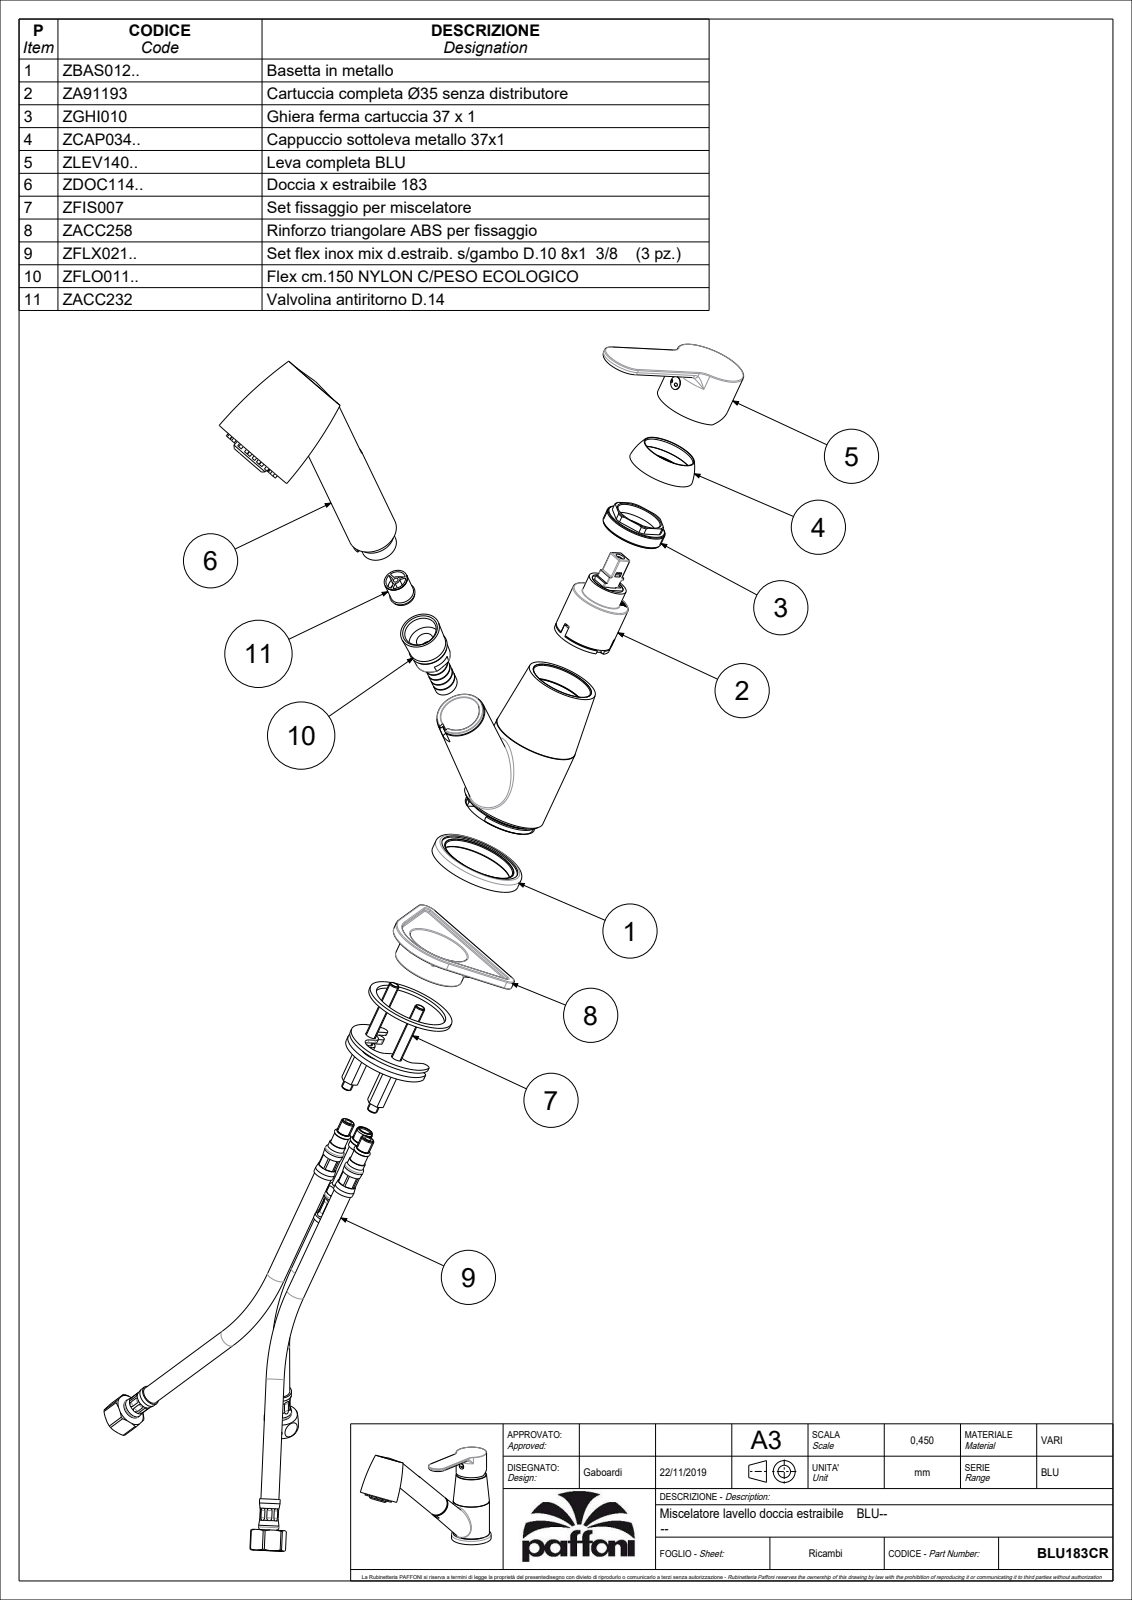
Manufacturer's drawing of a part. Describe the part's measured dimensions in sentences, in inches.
The part is named "BLU183CR". Its 3-D file was written by "CREO PARAMETRIC BY PTC INC, 2020044 (CONFIG_CONTROL_DESIGN)". It is 2 solids with 1166 faces: 470 planar, 440 cylindrical and 256 other. Overall it measures 9.855 by 6.832 by 2.154 inches. Its volume is 20.72 cubic inches and its surface area 182.2 square inches. Round holes: 32 of diameter 0.02, 5 of diameter 0.276, 3 of diameter 0.157, 3 of diameter 0.472, 2 of diameter 0.13, 2 of diameter 0.315, 2 of diameter 0.339, 1 of diameter 0.118, 1 of diameter 0.134, 1 of diameter 0.181, 1 of diameter 0.236, 1 of diameter 0.354. Round bosses or shafts: 32 of diameter 0.079, 2 of diameter 1.654, 2 of diameter 0.354, 2 of diameter 0.315, 2 of diameter 0.268, 2 of diameter 0.236, 1 of diameter 2.154, 1 of diameter 1.969. Partial cylindrical surfaces (rounded edges, fillets, slot ends): 41 of radius 0.02, 19 of radius 0.012, 10 of radius 0.047, 9 of radius 0.039, 3 of radius 0.098, 3 of radius 0.177, 2 of radius 0.063, 2 of radius 0.394. The main face-to-face distances are 0.039, 4.791, 0.433, 4.831, 0.035, 4.756, 4.795, 1.299, 0.295, 0.118. The hole center spacings are 0.591, 1.159, 0.159, 0.409, 0.541, 1.154, 1.289, 0.186.
